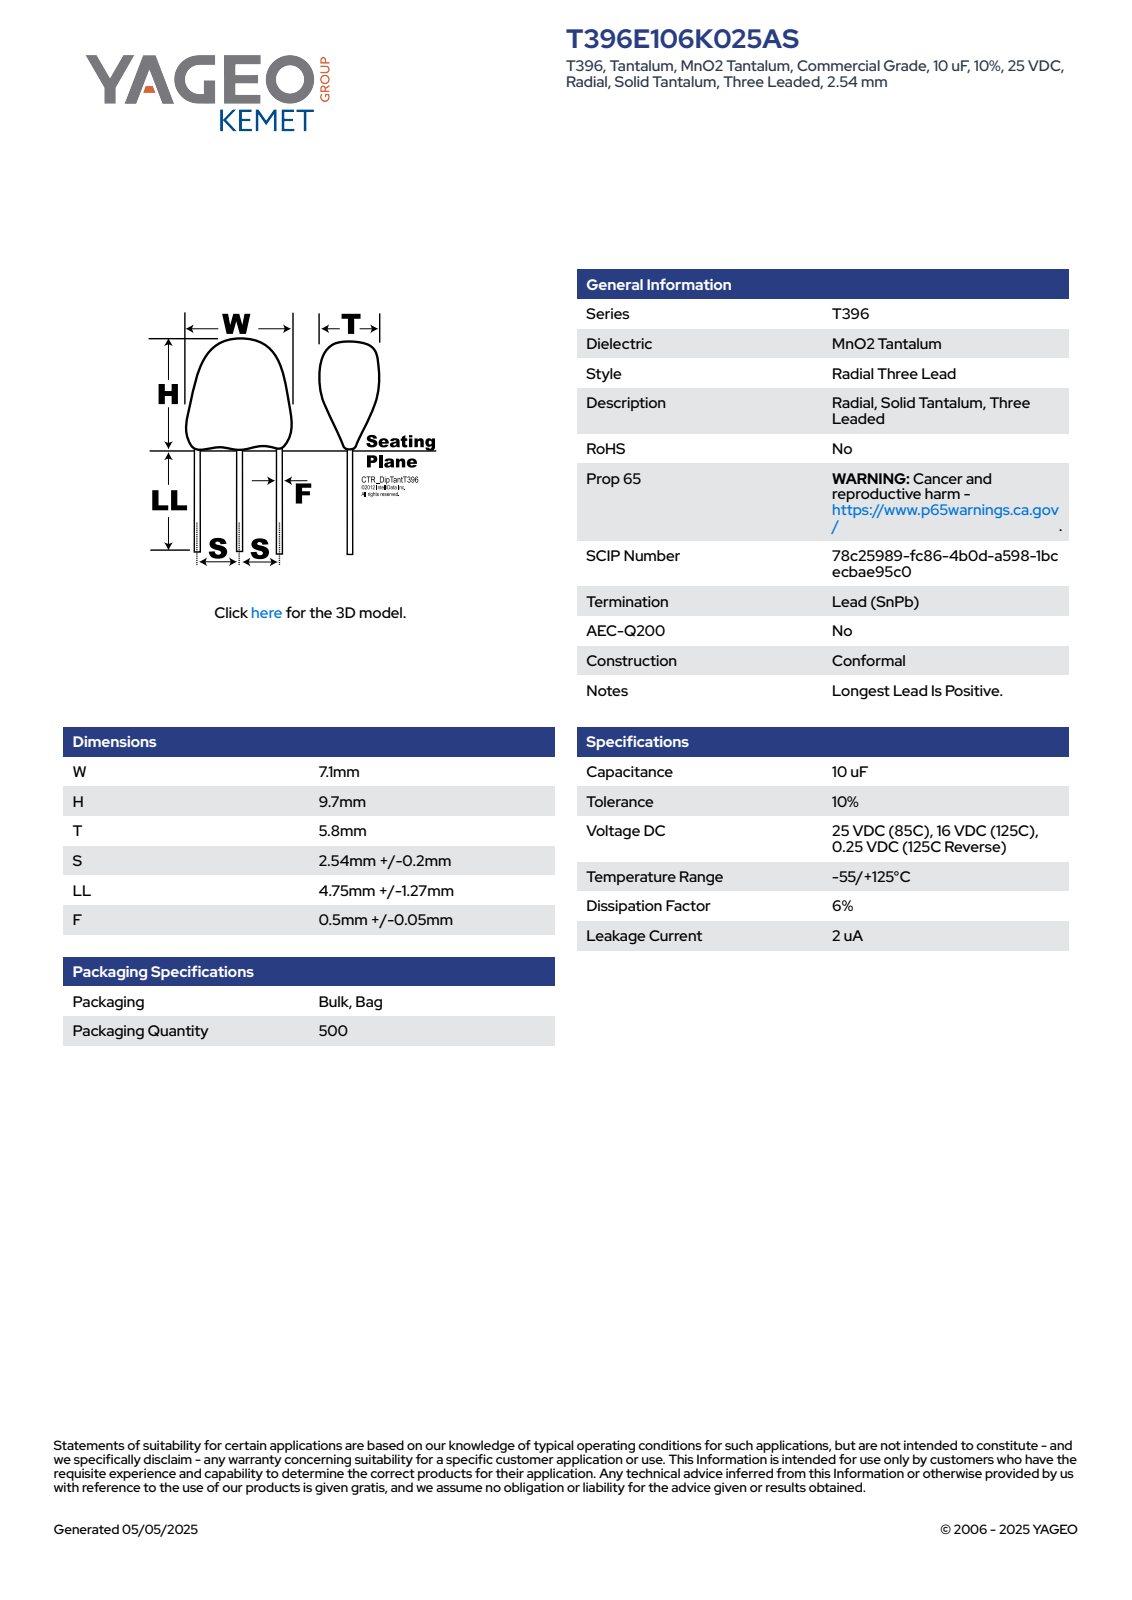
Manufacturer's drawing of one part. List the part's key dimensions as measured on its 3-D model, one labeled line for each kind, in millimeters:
Part name (STEP PRODUCT): CTR_T396_W7.1H9.7T5.8S2.54LL6.02F0.55
STEP written by: SolidWorks 2014 (AUTOMOTIVE_DESIGN)
Units: millimetres
Bodies: 4 solids, 88 faces (70 planar, 8 cylindrical, 10 other)
Overall size (bounding box): 15.72 × 7.1 × 4.8
Volume: 280 mm³ · Surface area: 270 mm²
Round bosses / shafts (diameter × count): ⌀0.55 ×3
Partial cylindrical surfaces — rounded edges, fillets, slot ends (radius × count): R5 ×2
Main face-to-face distances: 4.8, 7.1, 6.02, 0.91, 11.16, 5.14, 10.25, 4.23, 0.4, 3.72
